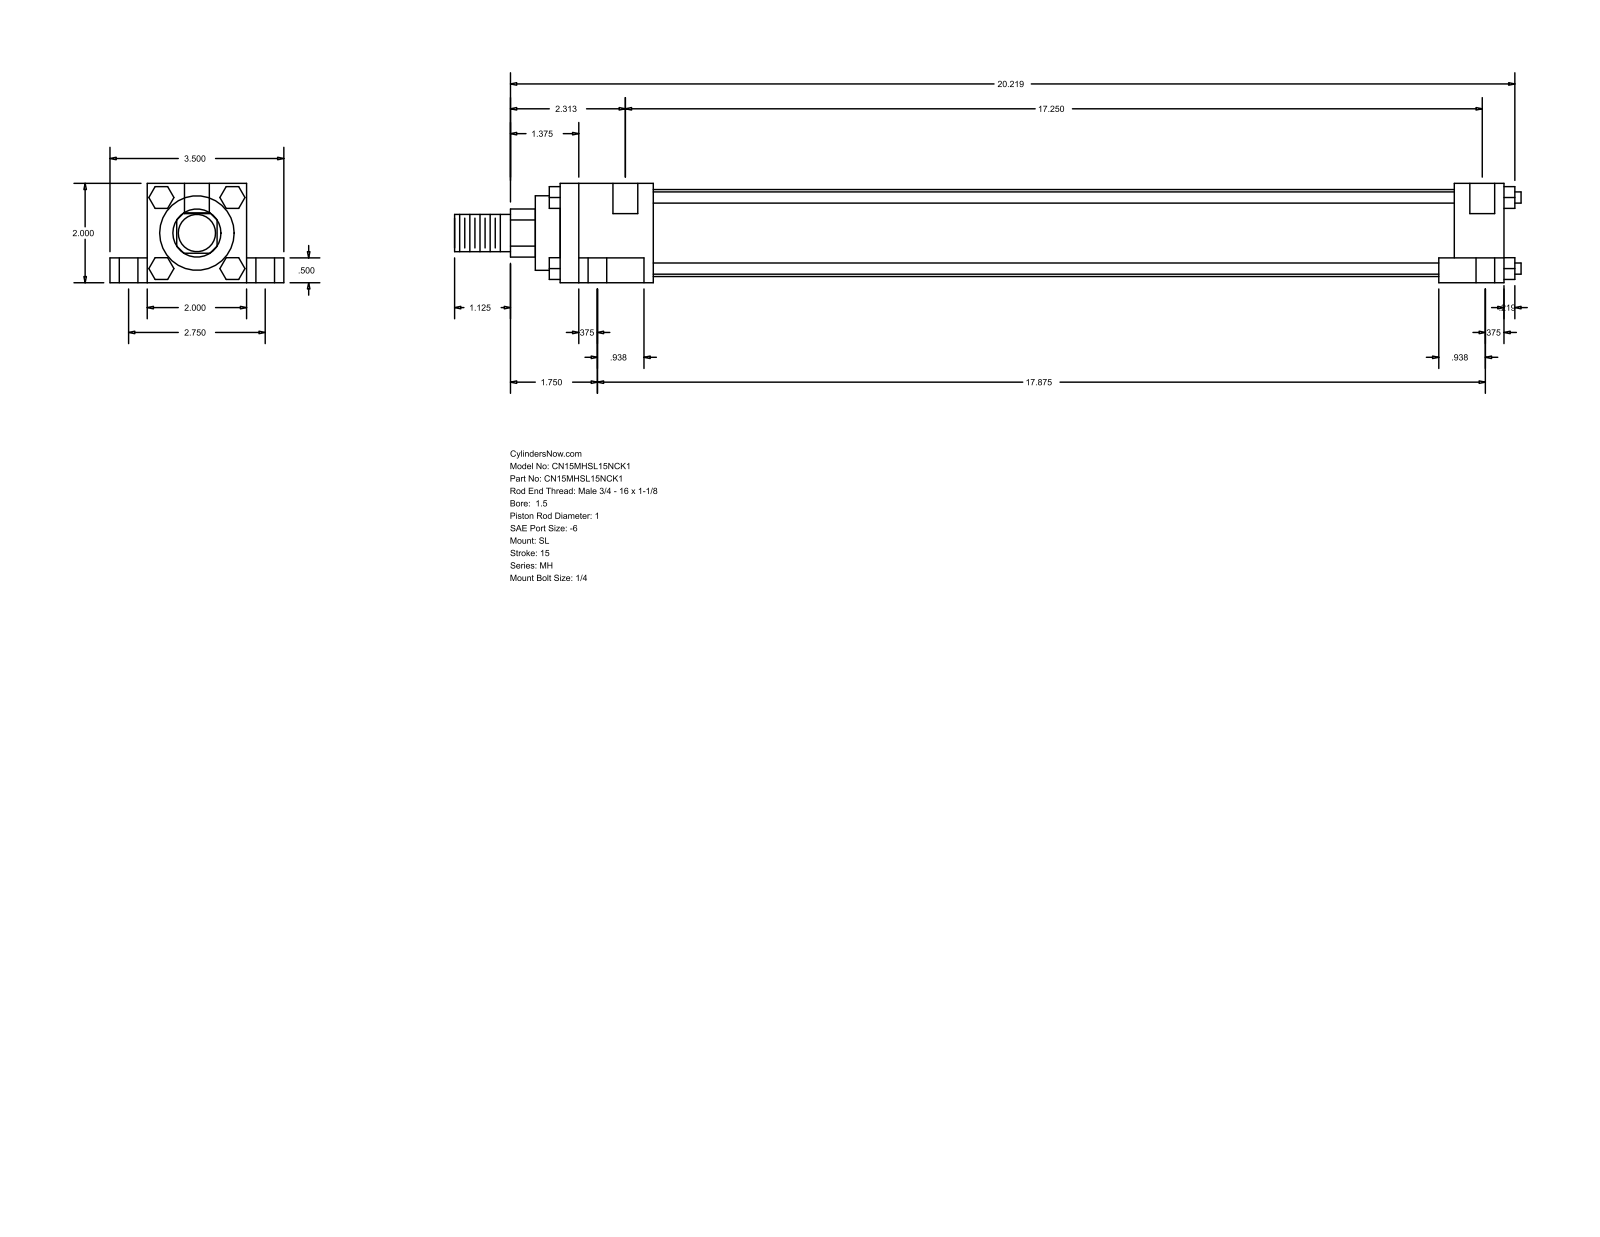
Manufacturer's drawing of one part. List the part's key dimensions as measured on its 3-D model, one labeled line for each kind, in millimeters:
Part name (STEP PRODUCT): MH_SL__0150_1
STEP written by: GSSL Pune (CONFIG_CONTROL_DESIGN)
Units: millimetres
Bodies: 0 solids, 148 faces (112 planar, 36 cylindrical, 0 other)
Overall size (bounding box): 545.31 × 88.9 × 50.8
Round holes (diameter × count): ⌀5.56 ×4, ⌀9.53 ×4, ⌀15.88 ×4, ⌀12.7 ×2
Round bosses / shafts (diameter × count): ⌀5.71 ×4, ⌀44.45 ×1, ⌀38.1 ×1, ⌀25.4 ×1, ⌀19.05 ×1
Partial cylindrical surfaces — rounded edges, fillets, slot ends (radius × count): R12.29 ×1
Main face-to-face distances: 50.8, 12.7, 38.1, 19.05, 69.85, 482.6, 25.4, 9.52, 33.34, 439.74
Hole centre spacings: 34.96, 36.64, 37.73, 69.84, 441.12, 441.33, 444.29, 453.79
